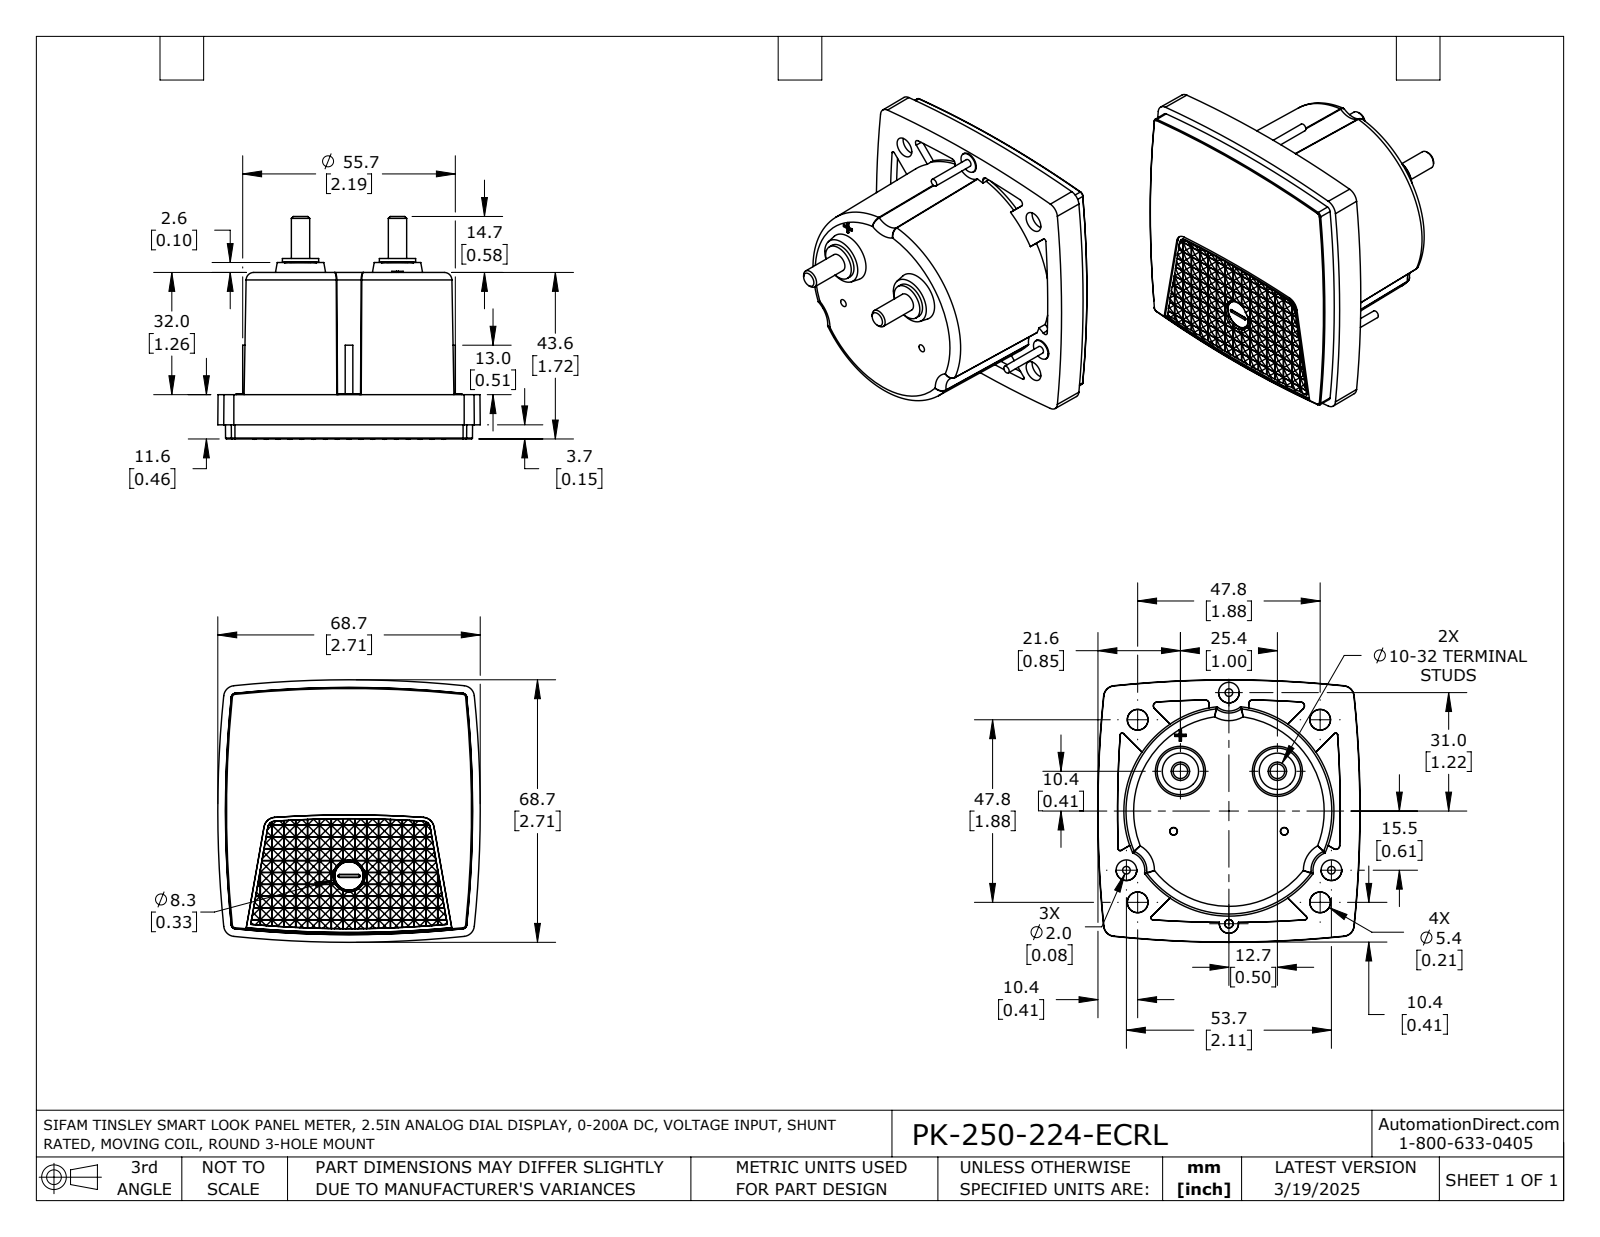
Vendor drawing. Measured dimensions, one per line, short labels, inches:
name: PK-250-224-ECRL
written by: SolidWorks 2021 (AUTOMOTIVE_DESIGN)
unit: in
bodies: 1 solid, 1550 faces (1165 planar, 265 cylindrical, 120 other)
size: 2.706 × 2.706 × 2.297
volume: 7.594 in³; area: 30.41 in²
bosses: 3× ⌀0.213, 3× ⌀0.079, 2× ⌀0.374, 2× ⌀0.189, 1× ⌀0.215
rounds: 2× R0.167, 1× R1.083
face distances: 1.717, 1.26, 0.457, 0.024, 0.087, 0.096, 0.311, 0.12, 0.072, 1.346
